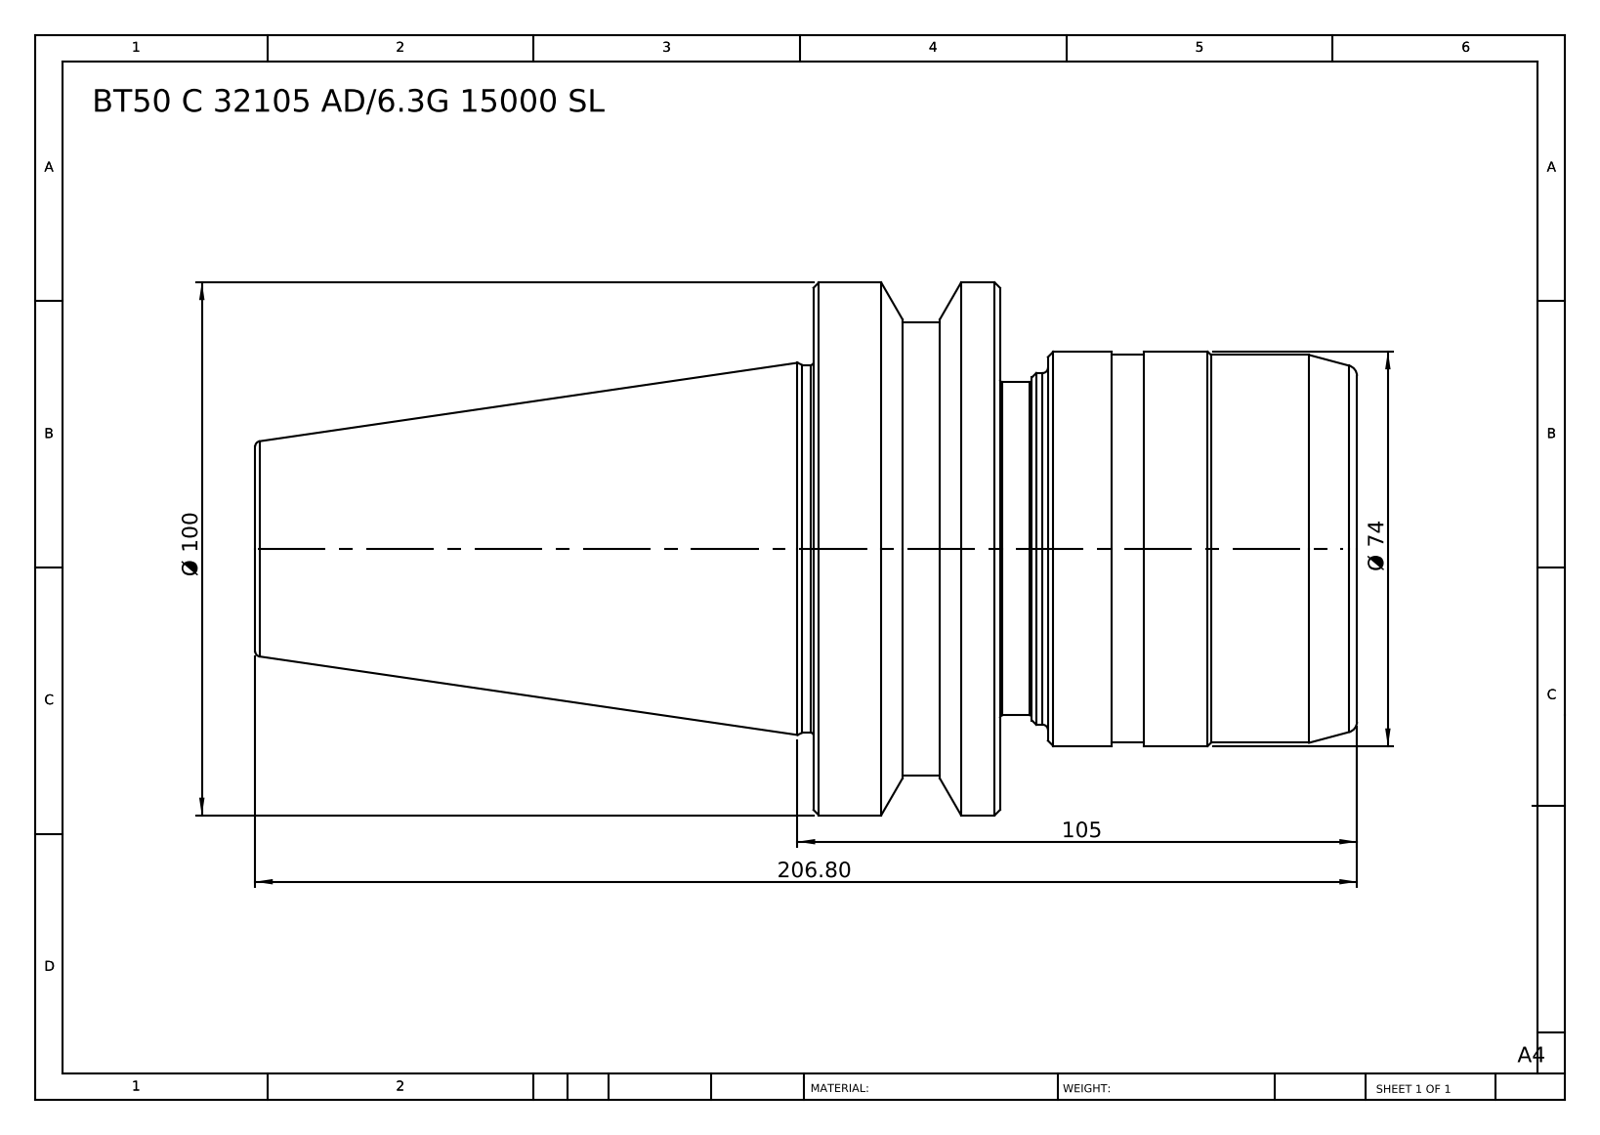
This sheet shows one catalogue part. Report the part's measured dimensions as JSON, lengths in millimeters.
{"part_name": "BT50 C32 105 AD-6.3G 15000 SL", "step_written_by": "SolidWorks 2014 (CONFIG_CONTROL_DESIGN)", "units": "millimeters", "bodies": {"solids": 1, "faces": 62, "planar": 10, "cylindrical": 20, "other": 32}, "overall_size": [206.8, 100, 100], "volume_mm3": 780844, "surface_area_mm2": 61221, "round_bosses_or_shafts": [[100, 1], [85, 1], [74, 1], [72.8, 1], [69, 1], [66, 1], [62.5, 1]], "face_to_face_distances": [35, 67, 102, 206.8, 139.8, 104.8, 58, 9, 44, 148.8]}
